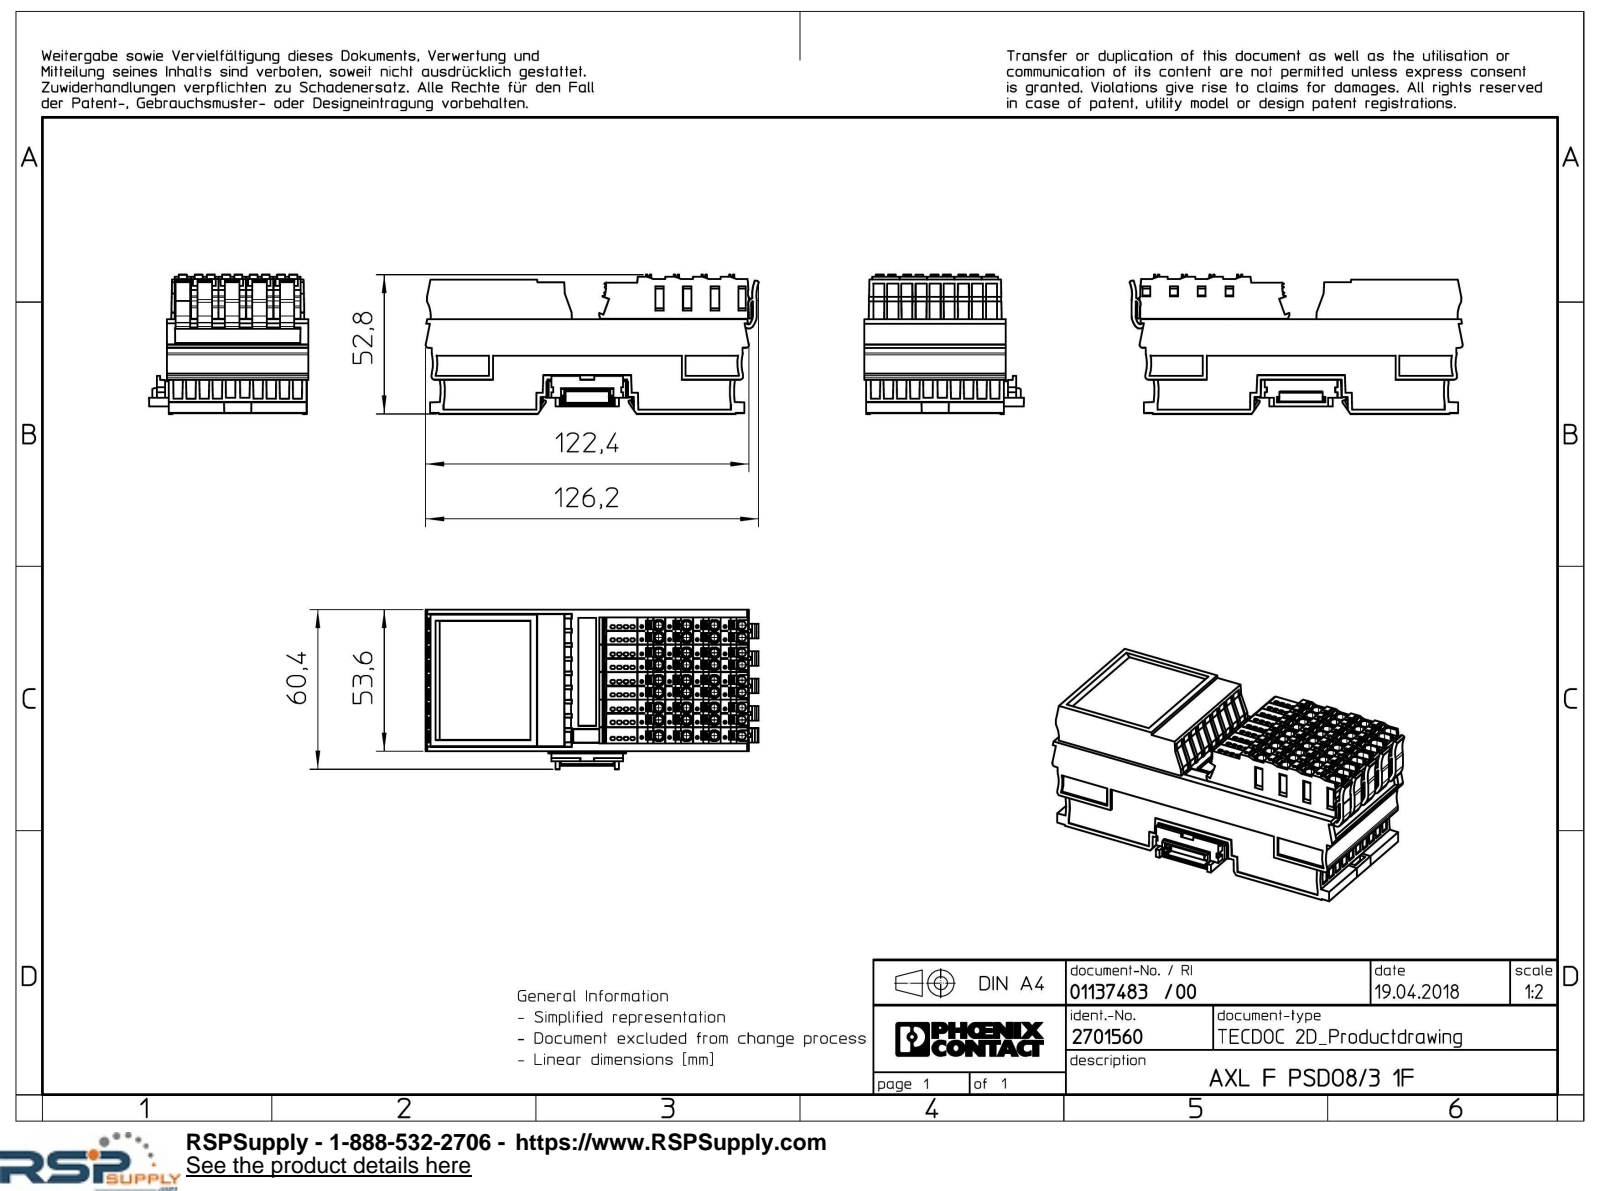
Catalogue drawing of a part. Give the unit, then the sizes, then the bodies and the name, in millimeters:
Units: millimetres
Overall size (bounding box): 126.17 × 60.4 × 52.75
Round holes (diameter × count): ⌀1.2 ×36
Partial cylindrical surfaces — rounded edges, fillets, slot ends (radius × count): R0.5 ×145, R1.5 ×126, R0.1 ×20, R1 ×10, R12.6 ×6, R3 ×5, R2 ×3, R0.3 ×2
Main face-to-face distances: 10.4, 20.8, 10.5, 0.9, 52.7, 31.2, 10.3, 35.45, 15, 20.7
Hole centre spacings: 14.78, 10.4, 10.5, 23.43, 11.63, 23.3, 18.64, 11.81
Volume: 282 146 mm³ · Surface area: 71 483 mm²
Bodies: 8 solids, 3724 faces (3023 planar, 621 cylindrical, 80 other)
Part name (STEP PRODUCT): FIBO_F_YE1018-select; FIBO_P_SP1.5_SINGLE_PWR...-select; FIBO_P_SP_TWIN_YE1018-select; FIBO-BS-F (+2 more)
STEP written by: Creo Elements/Direct Modeling 20.1A 29-Sep-2018 (C) Parametric Technology GmbH (AUTOMOTIVE_DESIGN)
